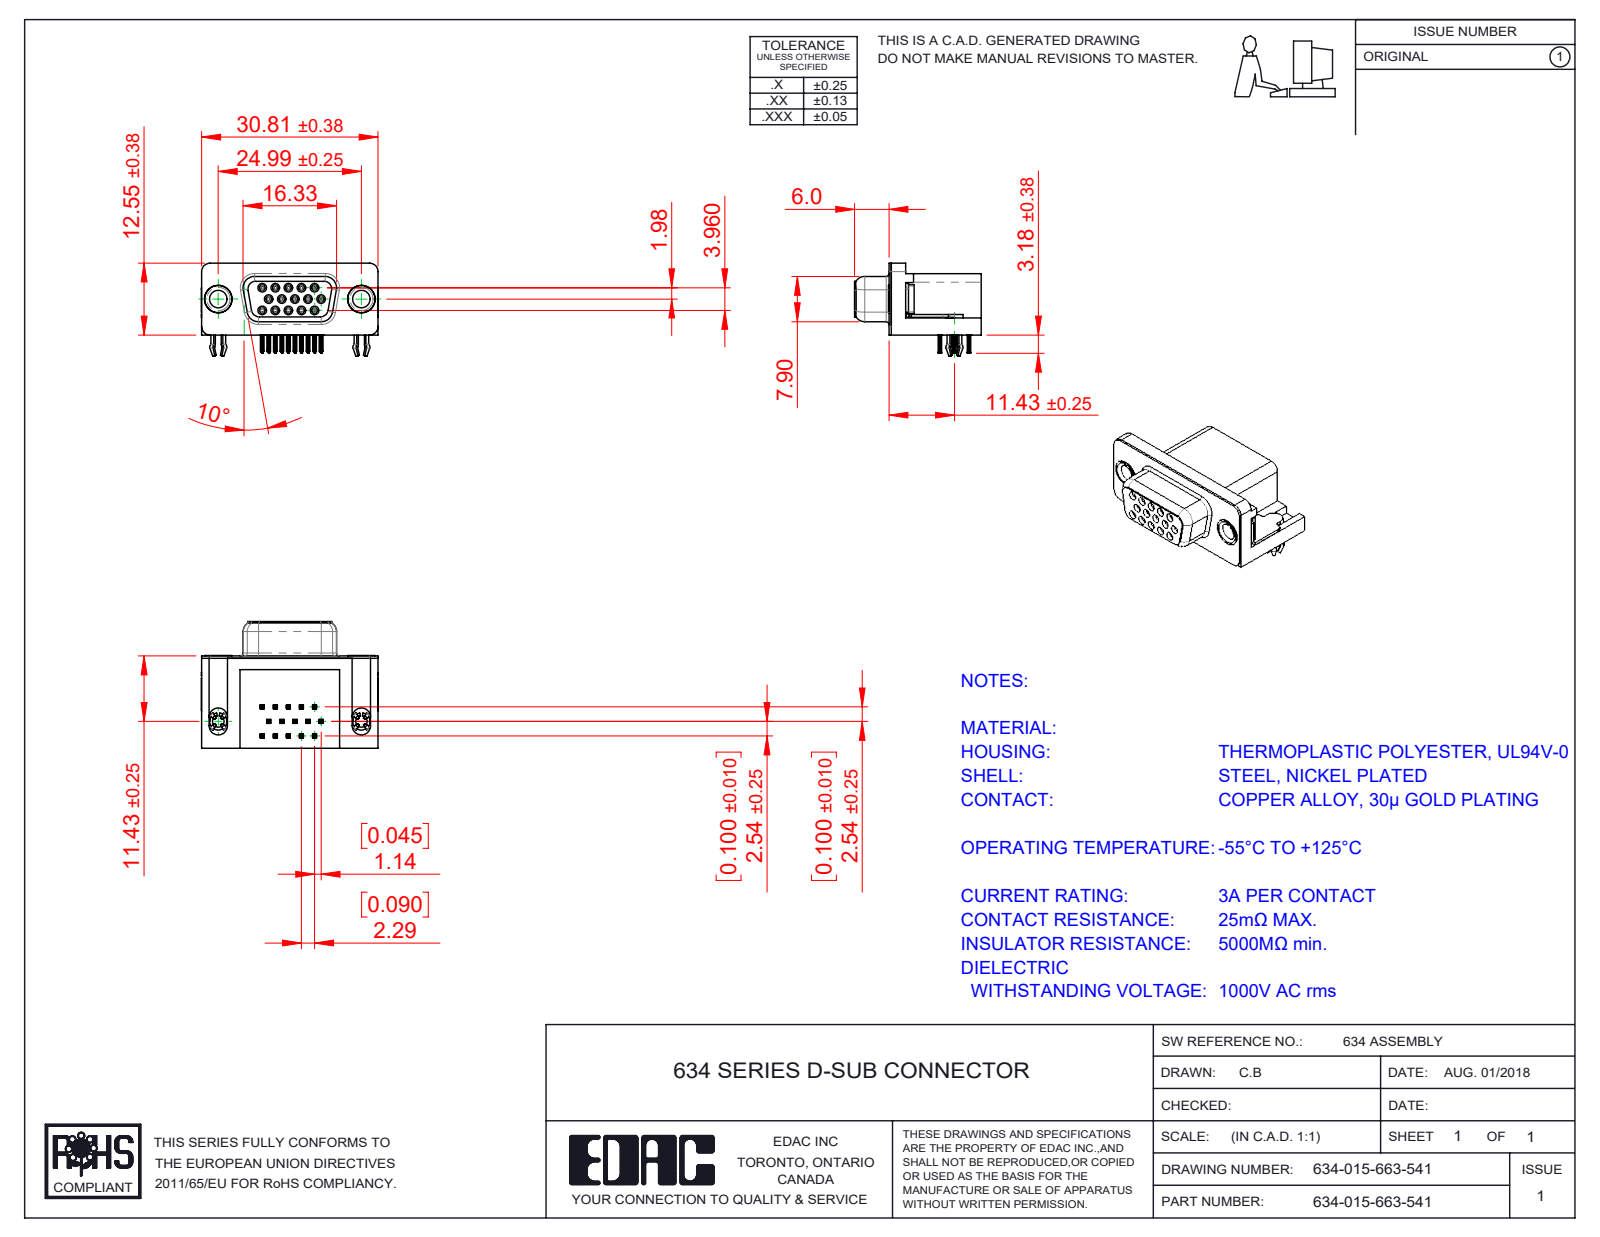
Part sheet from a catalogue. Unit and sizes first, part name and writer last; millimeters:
Units: millimetres
Overall size (bounding box): 30.89 × 22.1 × 16.25
Round holes (diameter × count): ⌀0.8 ×15, ⌀0.9 ×15, ⌀2 ×2, ⌀3.05 ×2, ⌀4 ×2, ⌀4.8 ×2, ⌀5 ×2
Round bosses / shafts (diameter × count): ⌀1.2 ×15, ⌀4.9 ×2, ⌀4.75 ×2, ⌀3.85 ×2, ⌀3 ×2
Partial cylindrical surfaces — rounded edges, fillets, slot ends (radius × count): R0.1 ×120, R0.15 ×60, R0.35 ×30, R1 ×19, R0.34 ×15, R0.25 ×12, R1.35 ×8, R1.6 ×8
Main face-to-face distances: 0.4, 10.35, 15.7, 16.1, 0.35, 2.5, 2.9, 6.4, 0.6, 10.7
Hole centre spacings: 2.29, 2.28, 3.96, 4.57, 6.05, 3.97, 4.58, 6.86
Volume: 4 551 mm³ · Surface area: 6 556 mm²
Bodies: 21 solids, 2501 faces (1108 planar, 587 cylindrical, 806 other)
Part name (STEP PRODUCT): Contact Bottom; 634 Shell; 634 Housing; Contact Top (+4 more)
STEP written by: SolidWorks 2016 (CONFIG_CONTROL_DESIGN)
